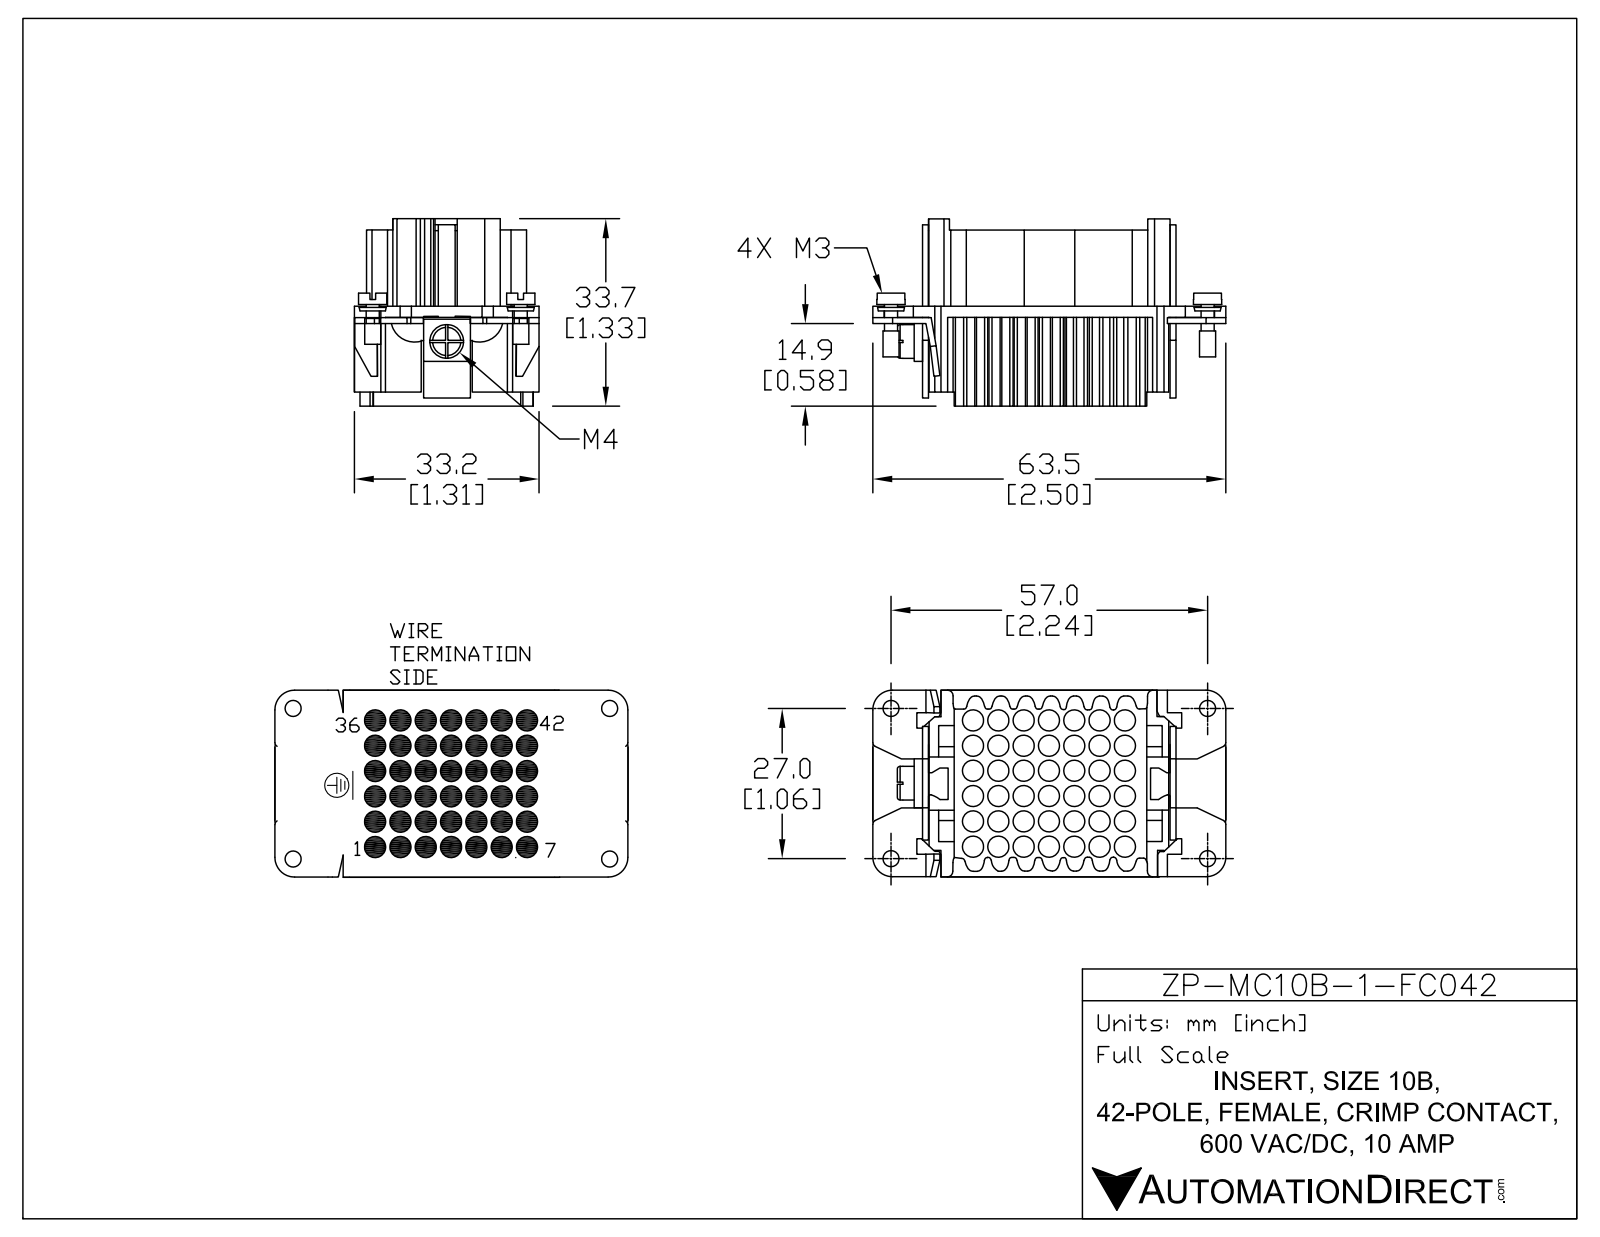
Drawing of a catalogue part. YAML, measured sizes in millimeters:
part_name: "ZP-10B-42-FC-INSERT"
step_written_by: "SolidWorks 2011 (AUTOMOTIVE_DESIGN)"
units: millimeters
bodies: {solids: 7, faces: 517, planar: 339, cylindrical: 81, other: 97}
overall_size: [62.75, 36, 33.26]
volume: 23431
surface_area: 30572
round_holes:
  - {diameter: 3.75, count: 42}
  - {diameter: 2.5, count: 4}
  - {diameter: 3, count: 1}
round_bosses_or_shafts:
  - {diameter: 5.02, count: 4}
  - {diameter: 2.85, count: 4}
  - {diameter: 2.32, count: 4}
  - {diameter: 6, count: 1}
partial_cylinders:
  - {radius: 0.75, count: 4}
  - {radius: 3.5, count: 4}
  - {radius: 0.68, count: 2}
  - {radius: 5.75, count: 2}
  - {radius: 2.33, count: 1}
  - {radius: 2.44, count: 1}
face_to_face_distances: [1.05, 2, 16, 18, 20, 14, 34, 2.04, 43.99, 16.04]
hole_center_spacings: [10.06, 4.5, 14.23, 6.36, 9, 16.22, 13.5, 18.55]
